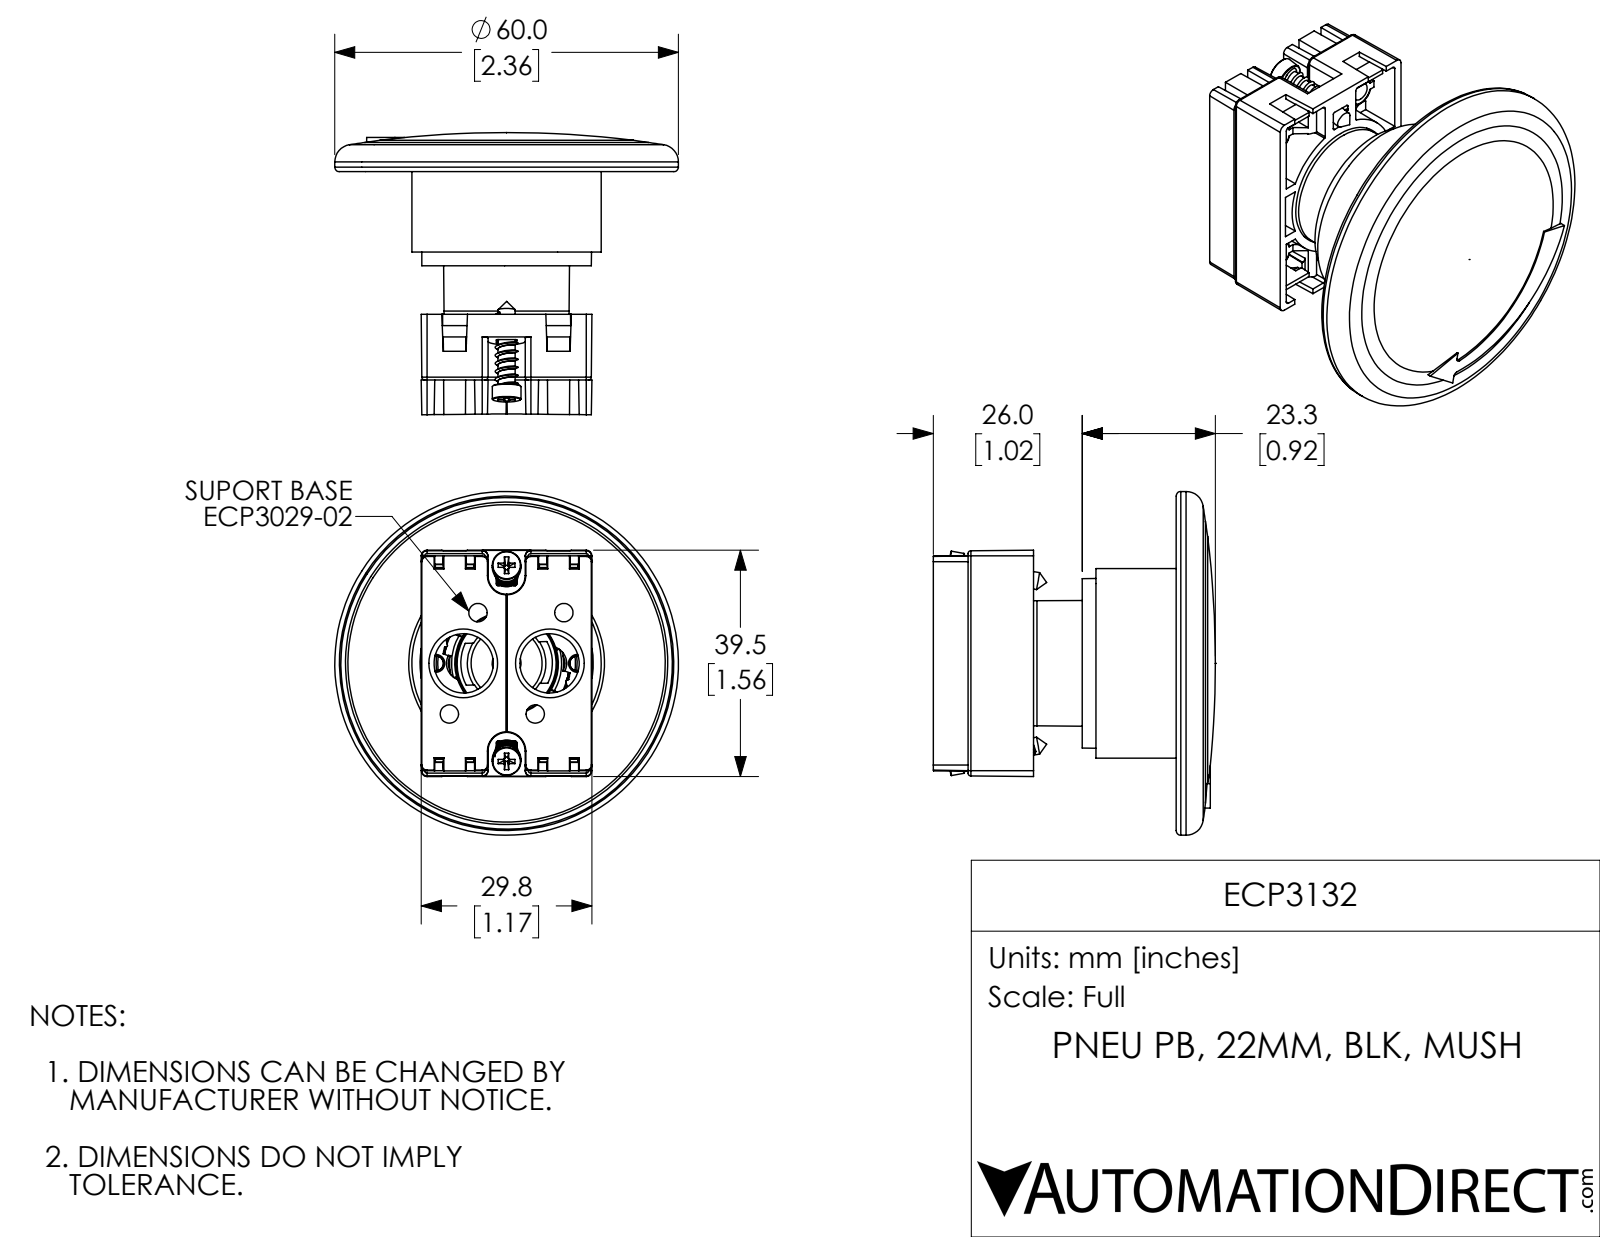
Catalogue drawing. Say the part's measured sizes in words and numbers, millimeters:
The part is named "ECP3132". Its 3-D file was written by "SolidWorks 2017 (AUTOMOTIVE_DESIGN)". It is 7 solids with 830 faces: 374 planar, 157 cylindrical and 299 other. Overall it measures 60 by 60 by 49.3 millimeters. Its volume is 30 480 cubic millimeters and its surface area 28 070 square millimeters. Round holes: 4 of diameter 2.1, 2 of diameter 10.3, 1 of diameter 2.6, 1 of diameter 3, 1 of diameter 17.7, 1 of diameter 19.2, 1 of diameter 22.7, 1 of diameter 30.3, 1 of diameter 56.3. Round bosses or shafts: 2 of diameter 5, 2 of diameter 3, 1 of diameter 60, 1 of diameter 33.1, 1 of diameter 21.8, 1 of diameter 19.2, 1 of diameter 13.7, 1 of diameter 12.4. Partial cylindrical surfaces (rounded edges, fillets, slot ends): 18 of radius 0.5, 8 of radius 0.2, 8 of radius 0.3, 4 of radius 0.2, 4 of radius 1, 2 of radius 0.2, 2 of radius 0.6, 2 of radius 3. The main face-to-face distances are 30.3, 1.7, 18.2, 18.8, 11.5, 14.9, 13.2, 34.8, 16, 4.5. The hole center spacings are 7.7, 13.7, 20.8, 7.5, 12, 24.7, 27.5, 15.
